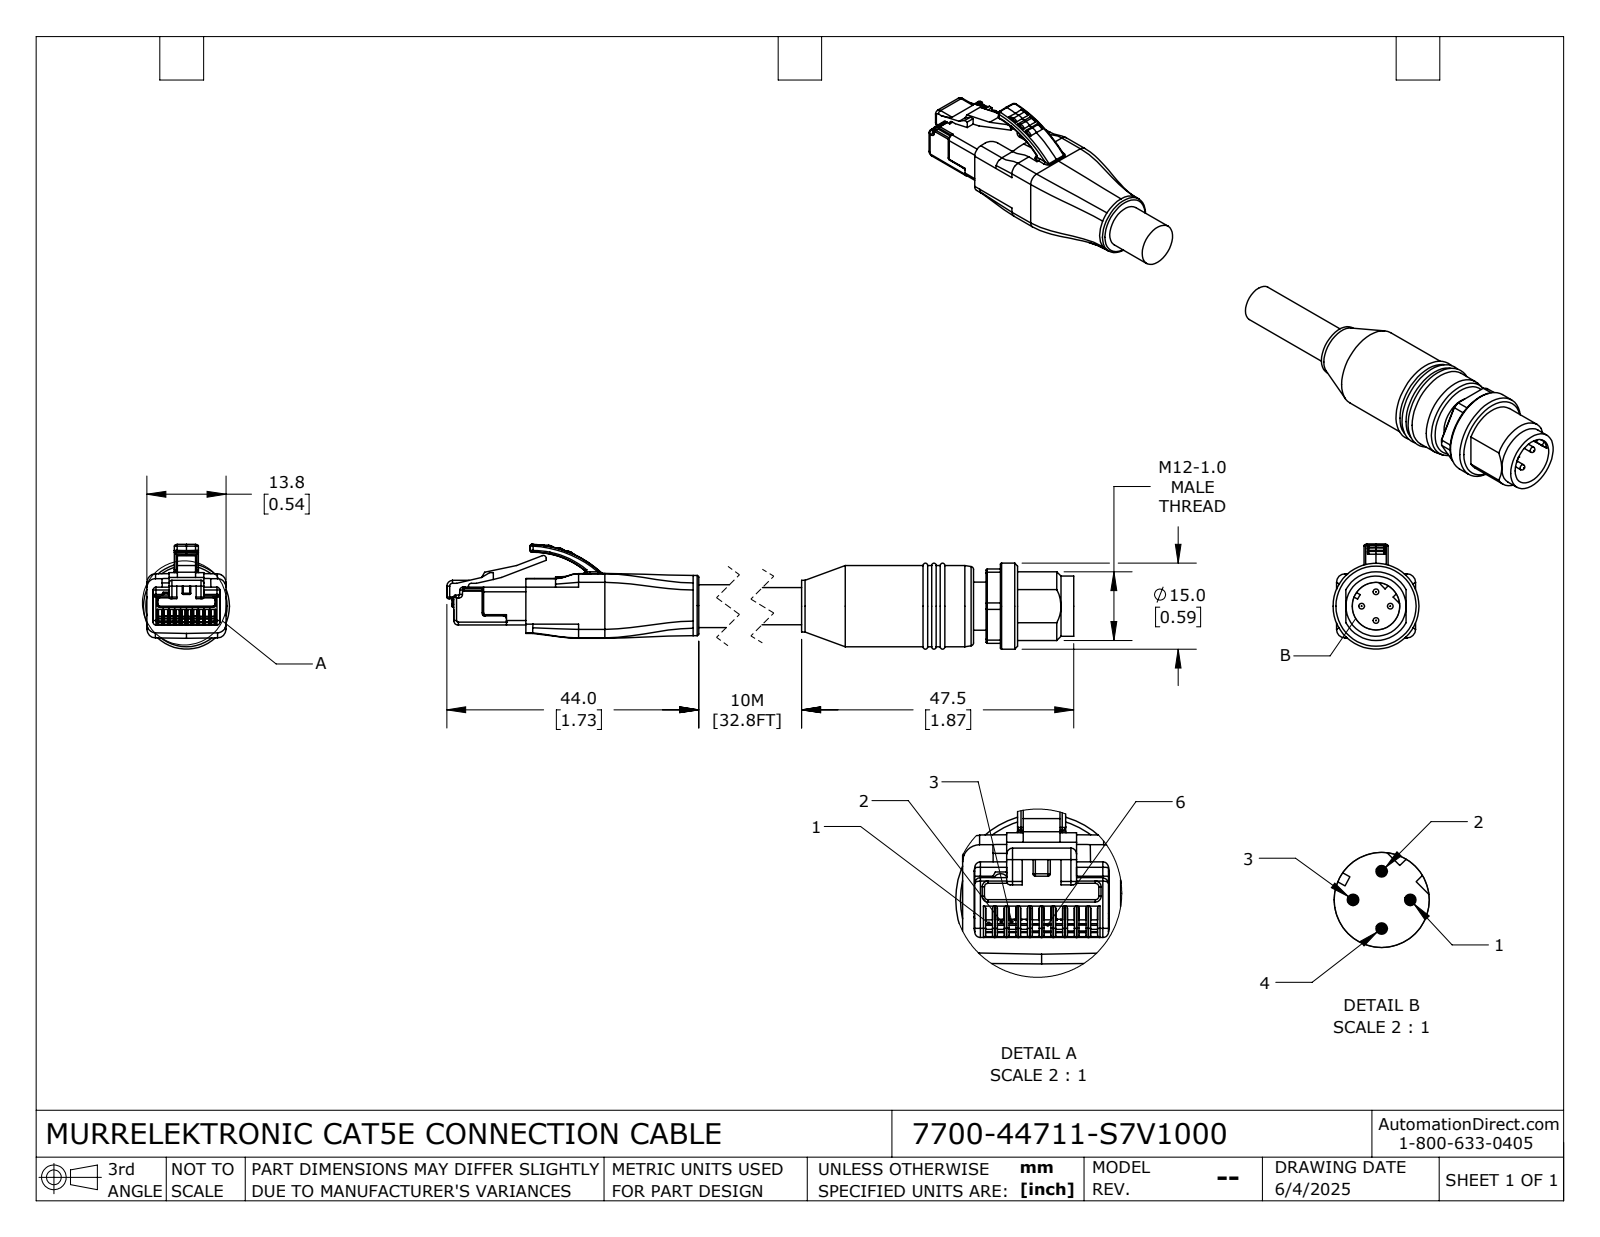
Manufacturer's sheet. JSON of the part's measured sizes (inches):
{"part_name": "7700-44711-S7V1000_MALE; 7700-44711-S7V1000_RJ45; 7700-44711-S7V1000", "step_written_by": "SolidWorks 2024 (CONFIG_CONTROL_DESIGN)", "units": "inches", "bodies": {"solids": 2, "faces": 757, "planar": 357, "cylindrical": 235, "other": 165}, "overall_size": [5.689, 0.72, 0.591], "volume_in3": 0.725, "surface_area_in2": 8.951, "round_holes": [[0.327, 1]], "round_bosses_or_shafts": [[0.039, 4], [0.413, 2], [0.591, 1], [0.559, 1], [0.354, 1], [0.331, 1], [0.295, 1], [0.256, 1]], "partial_cylinders_radius": [[0.008, 61], [0.02, 25], [0.012, 14], [0.059, 9], [0.031, 5], [0.021, 2], [0.197, 2], [0.005, 1]], "face_to_face_distances": [0.543, 0.087, 0.065, 0.478, 0.04, 0.504, 0.025, 0.439, 0.386, 0.035]}
